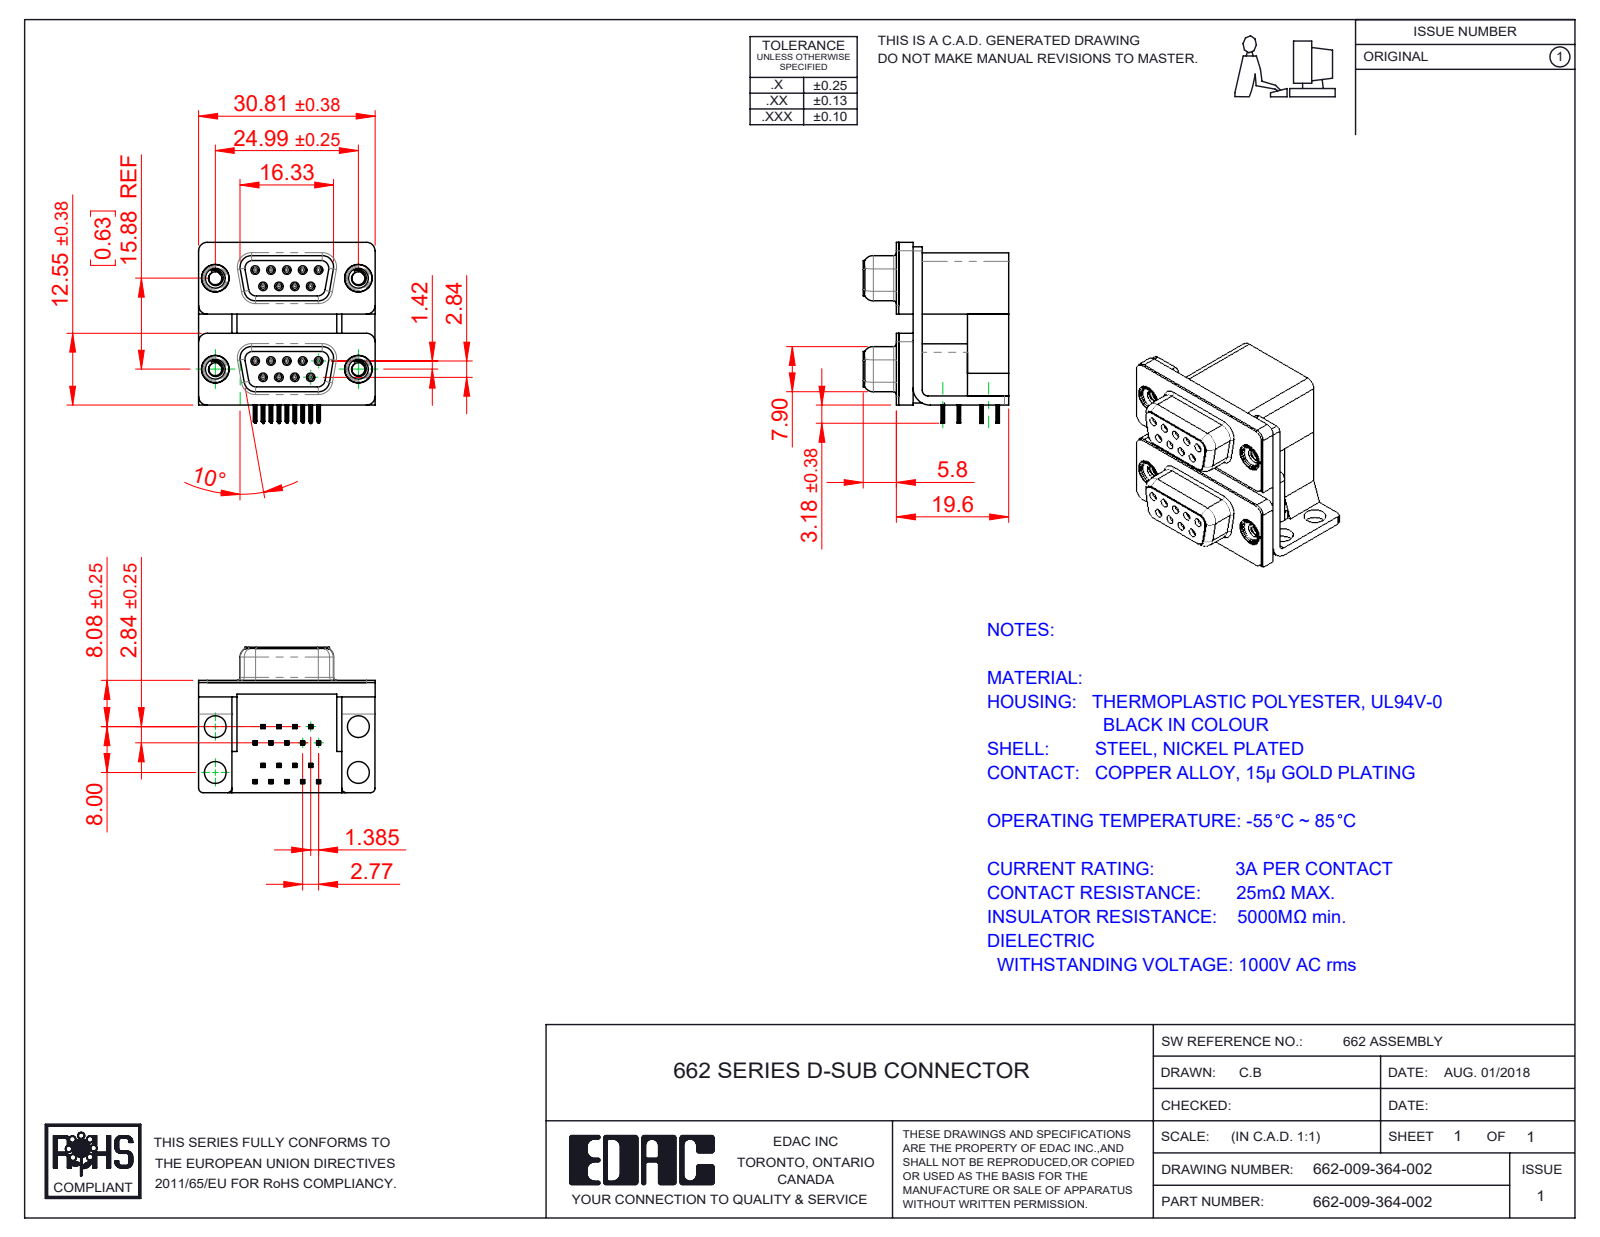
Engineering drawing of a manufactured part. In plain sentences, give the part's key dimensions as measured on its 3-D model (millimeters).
The part is named "662 Contact Top Lower; 662 Contact Bottom Lower; 662 Housing Spacer_09 Contacts L; 662 Mounting Bracket_NoneL (+7 more)". Its 3-D file was written by "SolidWorks 2020 (CONFIG_CONTROL_DESIGN)". It is 29 solids with 3110 faces: 1374 planar, 796 cylindrical and 940 other. Overall it measures 31.61 by 30.81 by 25.4 millimeters. Its volume is 10 830 cubic millimeters and its surface area 12 751 square millimeters. Round holes: 18 of diameter 0.8, 18 of diameter 0.9, 4 of diameter 2.26, 4 of diameter 3.5, 4 of diameter 3.8, 4 of diameter 4, 4 of diameter 4.8, 4 of diameter 5. Round bosses or shafts: 18 of diameter 1.2, 4 of diameter 4.9, 4 of diameter 4.75, 4 of diameter 3.9. Partial cylindrical surfaces (rounded edges, fillets, slot ends): 144 of radius 0.1, 72 of radius 0.15, 36 of radius 0.35, 18 of radius 0.34, 18 of radius 1.35, 12 of radius 1.5, 8 of radius 0.28, 8 of radius 0.5. The main face-to-face distances are 0.4, 2.5, 16.7, 19.2, 15.88, 2.9, 19.6, 7.2, 9.5, 12. The hole center spacings are 2.77, 3.16, 16.12, 5.54, 15.88, 16.82, 5.03, 3.15.
